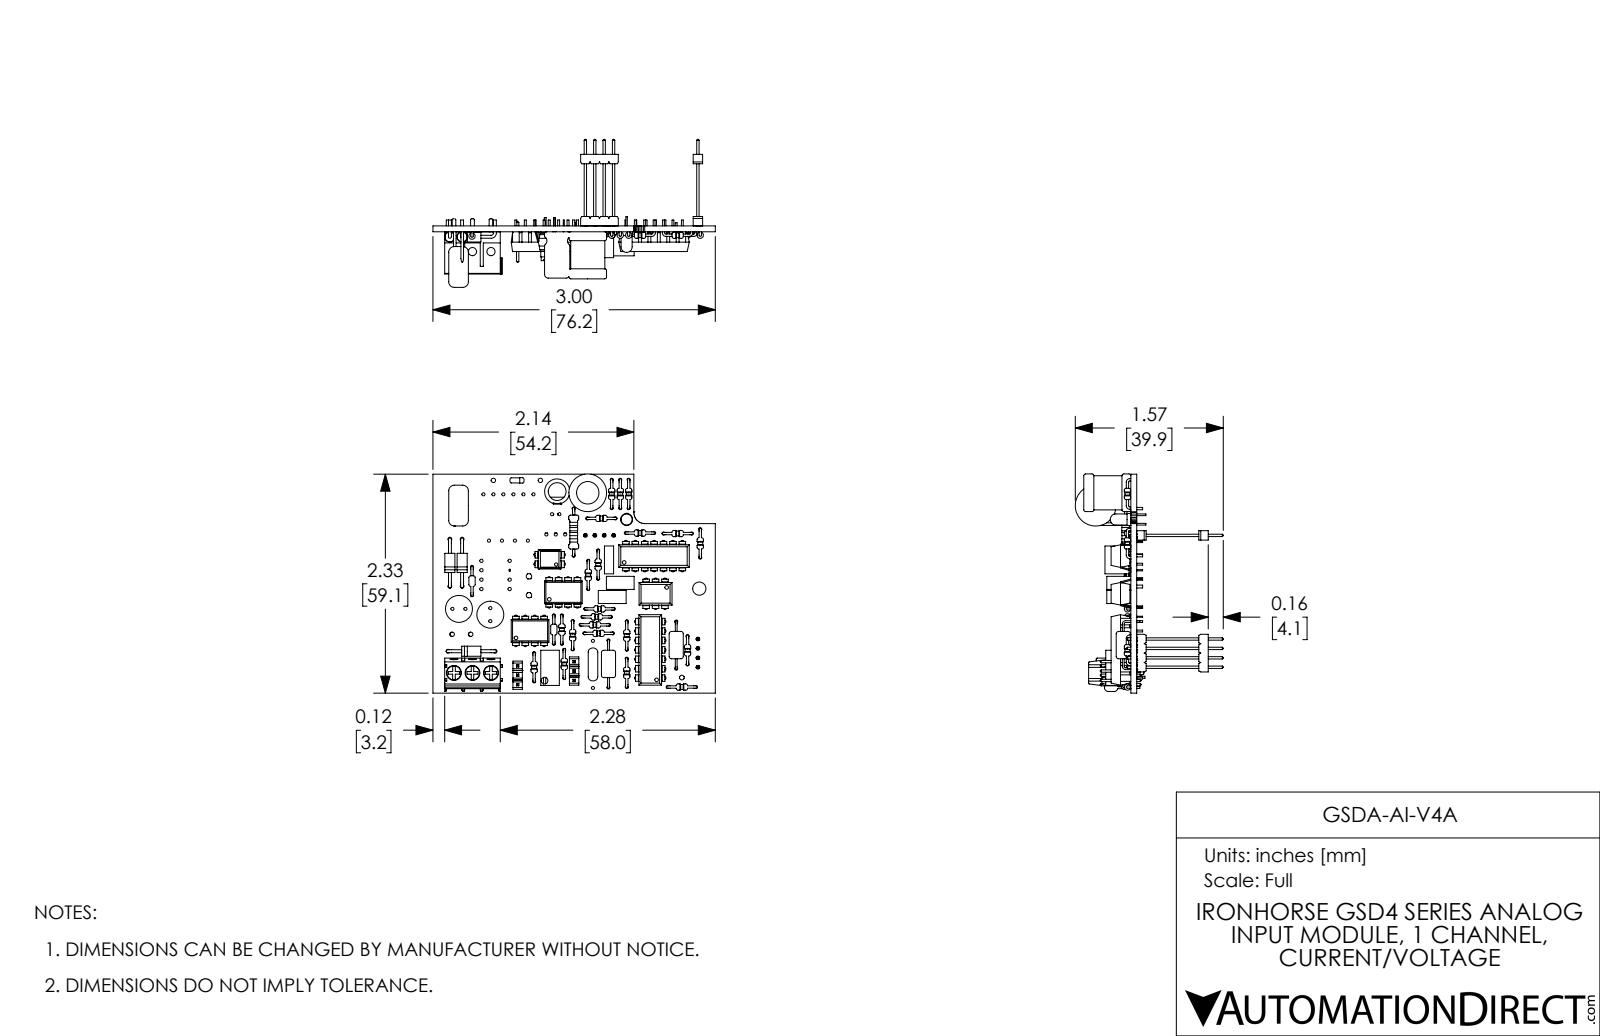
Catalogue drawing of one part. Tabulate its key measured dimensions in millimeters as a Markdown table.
| quantity | value |
| --- | --- |
| part name | GSDA-AI-V4A |
| STEP written by | SolidWorks 2017 (AUTOMOTIVE_DESIGN) |
| units | millimeters |
| bodies | 53 solids, 3005 faces (1639 planar, 975 cylindrical, 391 other) |
| overall size | 76.2 × 59.1 × 40 |
| volume | 13 200 mm³ |
| surface area | 18 010 mm² |
| round holes (diameter × count) | 0.8 × 80, 0.9 × 63, 1 × 20, 0.7 × 6, 1 × 5, 2.2 × 3, 4 × 3, 1 × 2, 1.2 × 2, 1.2 × 2, 1.4 × 2, 1.5 × 2 |
| round bosses / shafts (diameter × count) | 0.6 × 72, 1.7 × 22, 1.3 × 20, 0.6 × 14, 0.5 × 8, 0.5 × 6, 0.8 × 5, 0.8 × 4 |
| partial cylindrical surfaces (radius × count) | 0.3 × 15, 0.2 × 10, 0.2 × 4, 1.1 × 3, 1.5 × 3, 0.2 × 2, 0.6 × 2, 1 × 2 |
| main face-to-face distances | 1.6, 5.3, 1.8, 5.1, 6.9, 2.5, 6, 1.6, 0.9, 1.6 |
| hole center spacings | 2.5, 5, 5.1, 7.6, 8, 10.2, 30.4, 30.9 |
